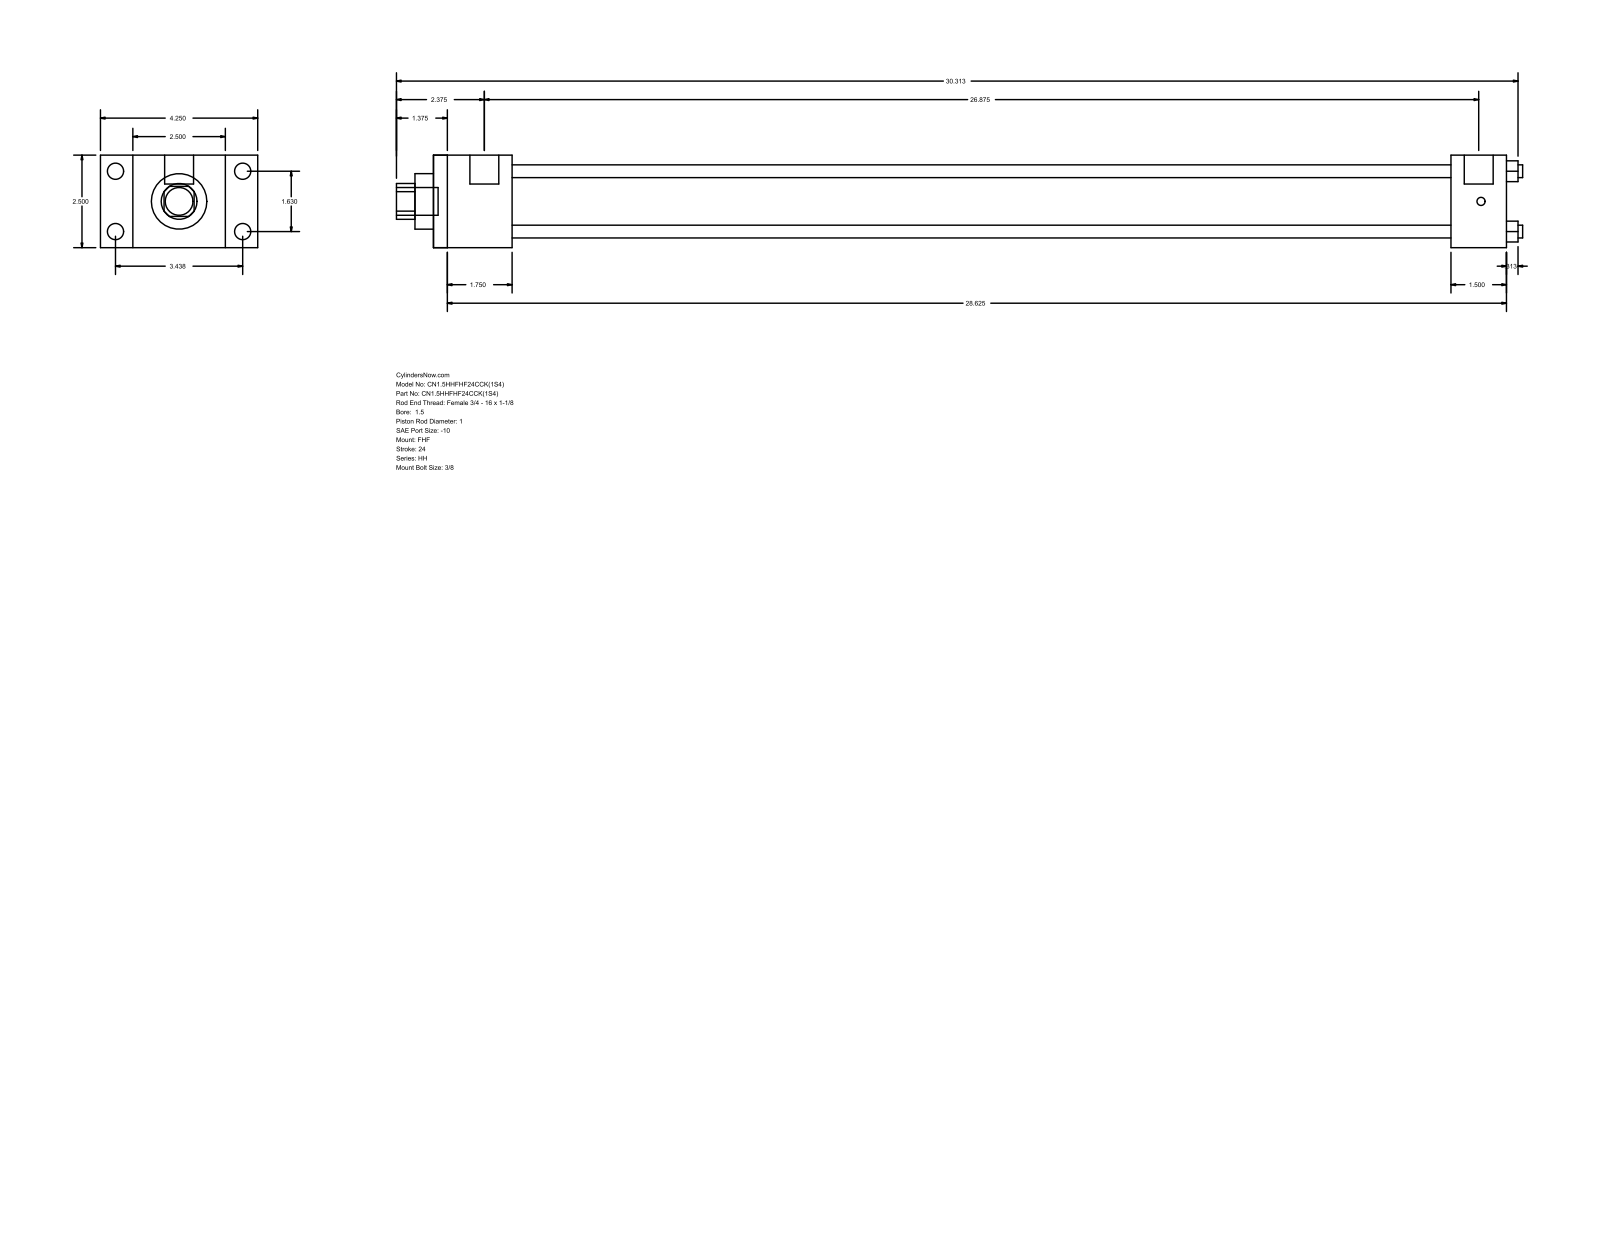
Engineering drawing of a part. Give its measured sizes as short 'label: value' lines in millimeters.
name: HH_FHF__0150_1
written by: GSSL Pune (CONFIG_CONTROL_DESIGN)
unit: mm
bodies: 0 solids, 88 faces (60 planar, 28 cylindrical, 0 other)
size: 773.11 × 107.95 × 63.5
holes: 4× ⌀8.76, 1× ⌀25.4, 1× ⌀38.1, 1× ⌀44.45
bosses: 4× ⌀11.13, 4× ⌀5.56, 2× ⌀19.84, 1× ⌀19.05
rounds: 1× R12.29
face distances: 63.5, 22.23, 85.73, 53.98, 107.96, 736.6, 682.62, 698.5, 644.52, 38.1
hole spacings: 29.27, 41.4, 58.55
